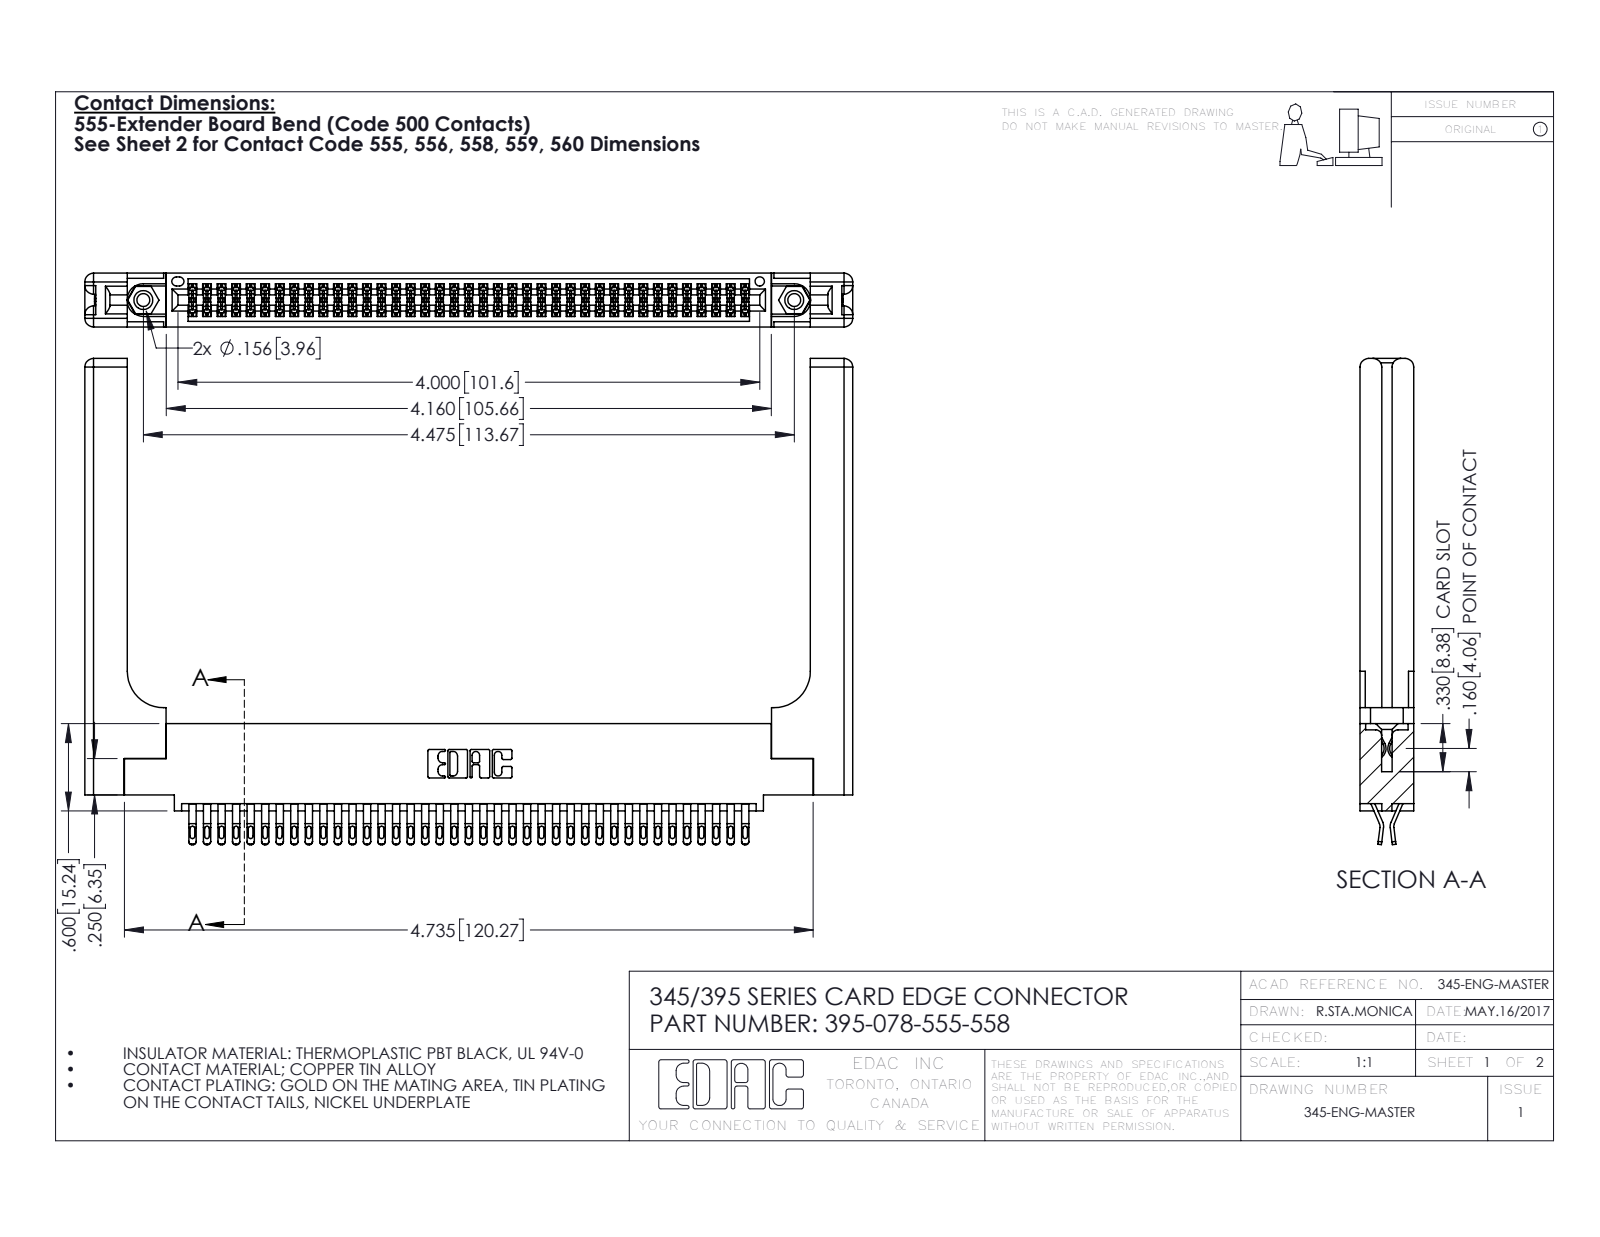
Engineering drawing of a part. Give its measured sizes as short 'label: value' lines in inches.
name: 345 Part_0.110 Offset - 0.156 Dia-TH; 345-250-001_345-250-001-102; 395-078-555-558; 345-292-001_555 Tail (+1 more)
written by: SolidWorks 2016 (CONFIG_CONTROL_DESIGN)
unit: in
bodies: 83 solids, 4754 faces (2650 planar, 2044 cylindrical, 60 other)
size: 5.279 × 3.342 × 0.37
volume: 1.32 in³; area: 39.24 in²
holes: 2× ⌀0.089, 2× ⌀0.125, 2× ⌀0.156, 1× ⌀0.064
bosses: 2× ⌀0.155
rounds: 195× R0.016, 156× R0.02, 117× R0.006, 22× R0.01, 16× R0.06, 6× R0.007, 6× R0.031, 3× R0.026
face distances: 0.072, 0.37, 0.298, 0.025, 0.2, 0.098, 0.272, 0.225, 0.148, 0.15
hole spacings: 0.27, 4.239, 4.475
